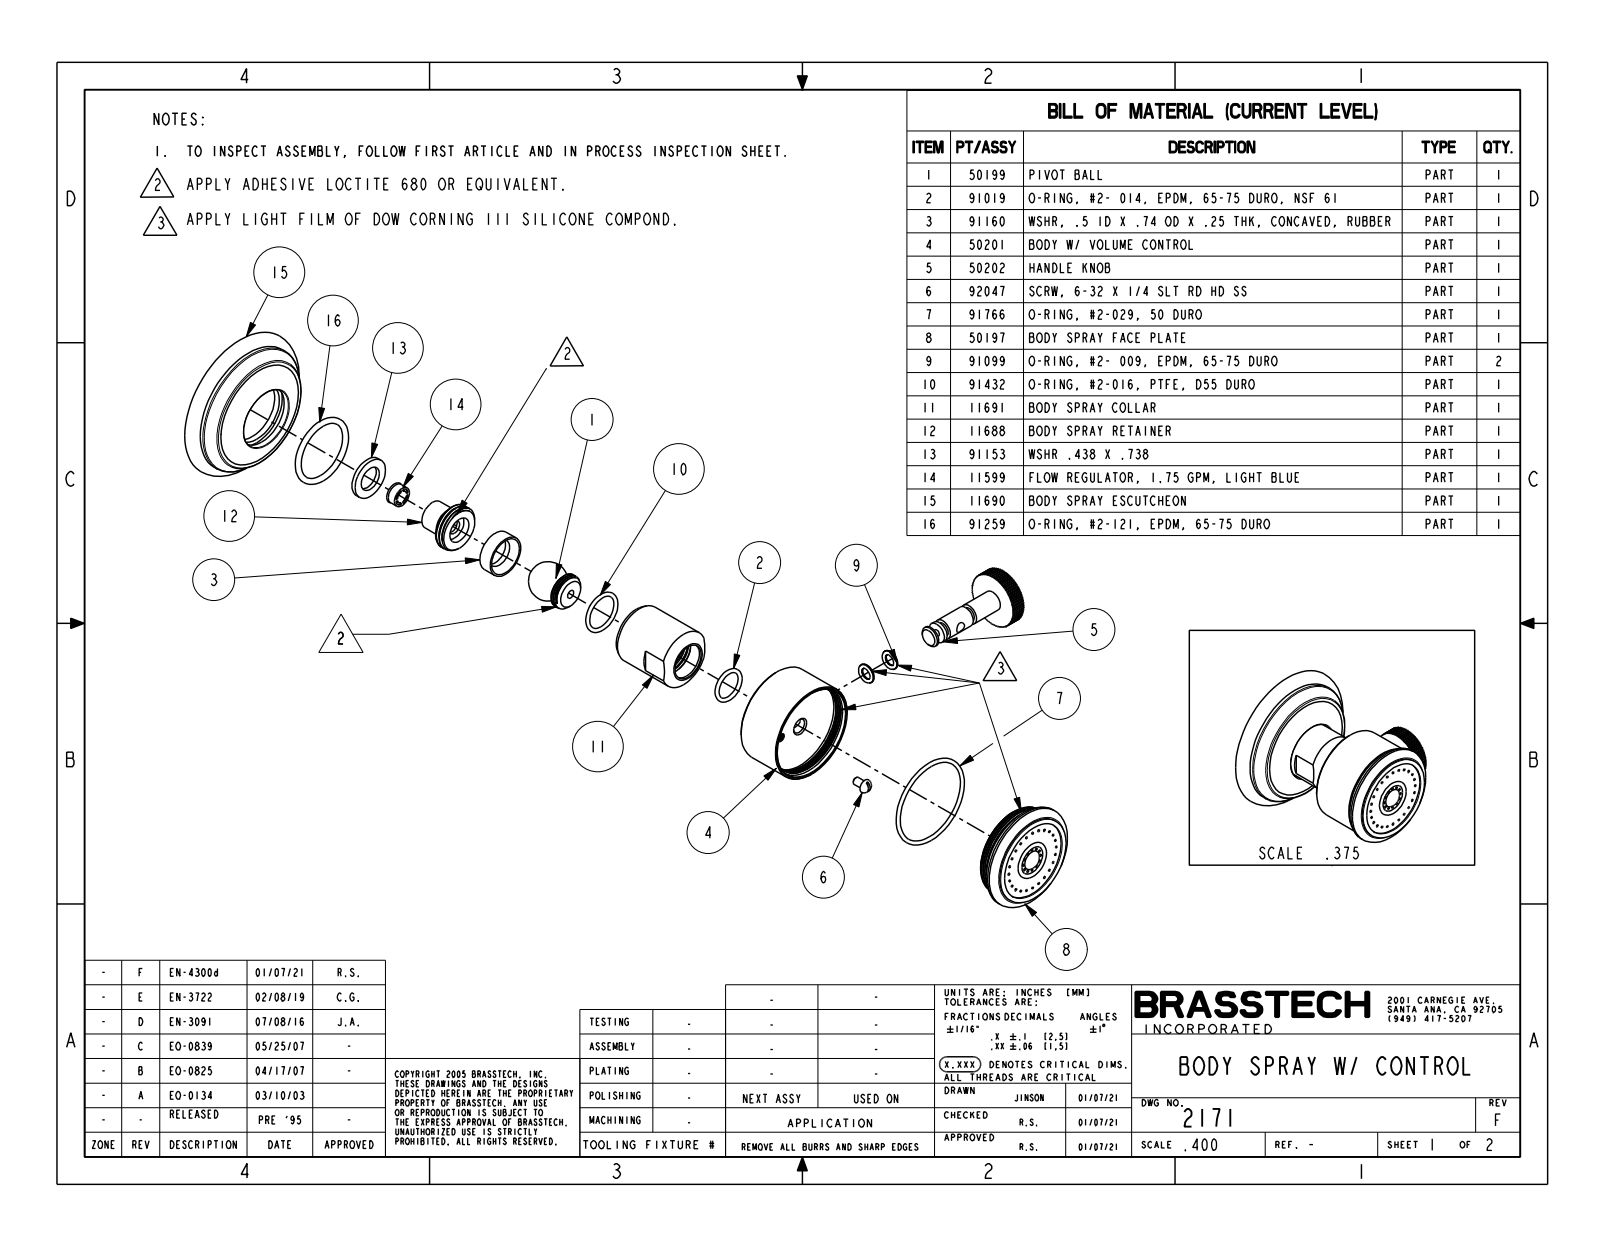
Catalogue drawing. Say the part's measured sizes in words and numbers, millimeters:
The part is named "2171". Its 3-D file was written by "CREO PARAMETRIC BY PTC INC, 2018400 (CONFIG_CONTROL_DESIGN)". It is 1 solid with 373 faces: 179 planar, 154 cylindrical and 40 other. Overall it measures 71.2 by 68.5 by 68.5 millimeters. Its volume is 98 190 cubic millimeters and its surface area 20 260 square millimeters. Round holes: 36 of diameter 1, 1 of diameter 27.7, 1 of diameter 35.9. Round bosses or shafts: 1 of diameter 59.3, 1 of diameter 44.2, 1 of diameter 39.9, 1 of diameter 27, 1 of diameter 22.2, 1 of diameter 9.4, 1 of diameter 8. Partial cylindrical surfaces (rounded edges, fillets, slot ends): 1 of radius 12.7. The main face-to-face distances are 40.5, 6.6, 35, 5.5, 11.9, 23.1, 28.5, 62.6, 50.6, 27.6. The hole center spacings are 9.1.
